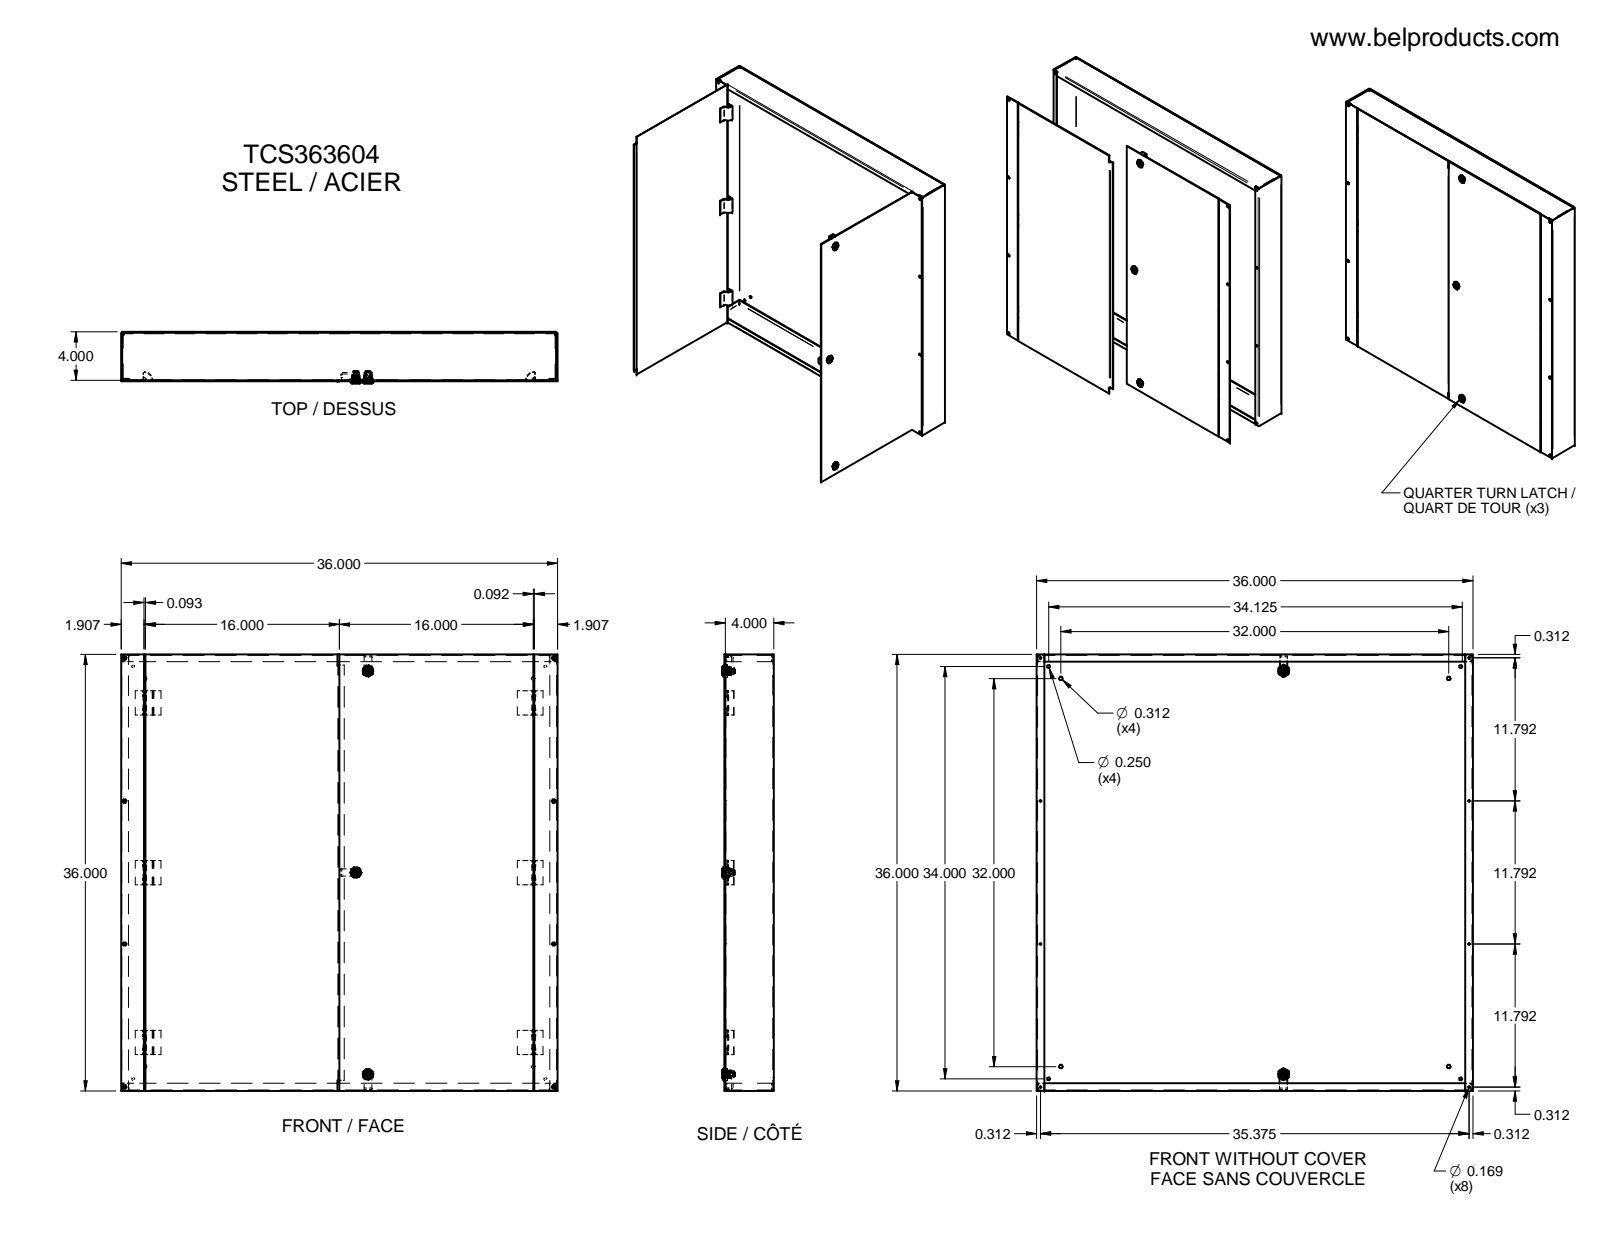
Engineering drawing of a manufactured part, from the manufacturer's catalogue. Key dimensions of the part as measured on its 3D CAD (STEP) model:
Part name (STEP PRODUCT): LOCK AVEC TOURNEVIS TYPE 4-12 SANS CAME; HOSING-oa0; INSERT POUR TOURNEVIS-oa1; NOIX DE FIXATION-oa2 (+8 more)
STEP written by: Unknown (AUTOMOTIVE_DESIGN)
Units: millimetres
Bodies: 46 solids, 1693 faces (850 planar, 421 cylindrical, 422 other)
Overall size (bounding box): 914.4 × 914.4 × 107.97
Volume: 4 097 000 mm³ · Surface area: 4 351 000 mm²
Round holes (diameter × count): ⌀7.92 ×12, ⌀4.29 ×8, ⌀6.35 ×4, ⌀9.1 ×3, ⌀11.18 ×3, ⌀12.83 ×3, ⌀15.8 ×3, ⌀17.46 ×3, ⌀3.81 ×2, ⌀6.99 ×2
Round bosses / shafts (diameter × count): ⌀22.86 ×3, ⌀22.61 ×3, ⌀15.75 ×3, ⌀12.95 ×3, ⌀12.62 ×3, ⌀12.19 ×3, ⌀11.86 ×3, ⌀10.08 ×3
Partial cylindrical surfaces — rounded edges, fillets, slot ends (radius × count): R9.53 ×34, R0.25 ×24, R0.81 ×17, R2.72 ×14, R9.42 ×6, R1.52 ×4, R3.05 ×4, R3.48 ×3
Main face-to-face distances: 1.91, 101.6, 99.69, 103.51, 1.9, 912.5, 914.4, 910.6, 101.59, 103.5
Hole centre spacings: 838.58, 856.73, 881.23, 898.52, 947.12, 24.69, 35.92, 60.61
